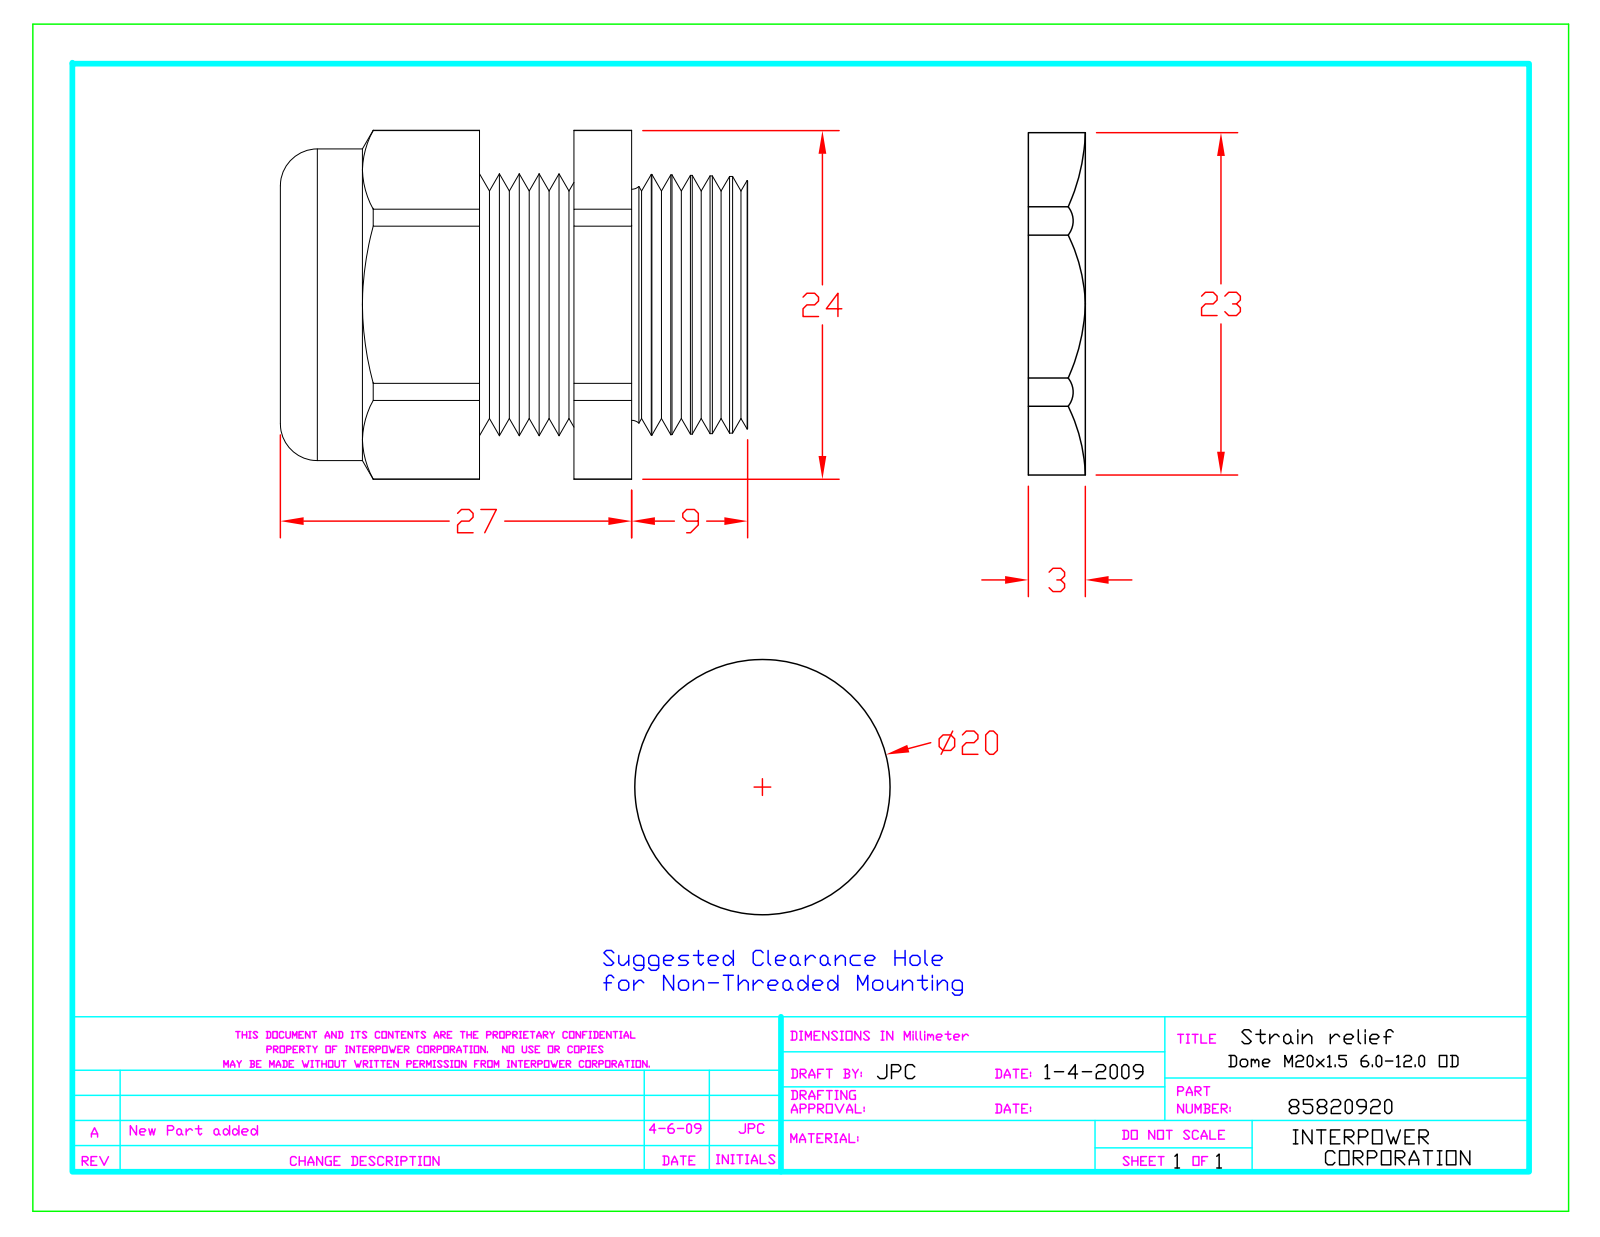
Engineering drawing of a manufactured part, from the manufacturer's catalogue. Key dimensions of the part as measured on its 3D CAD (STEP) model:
Part name (STEP PRODUCT): CD20MA
STEP written by: SolidWorks 2007 (CONFIG_CONTROL_DESIGN)
Units: inches
Bodies: 2 solids, 116 faces (20 planar, 24 cylindrical, 72 other)
Overall size (bounding box): 1.41 × 1.053 × 0.94
Volume: 0.514 in³ · Surface area: 10.49 in²
Round holes (diameter × count): ⌀0.51 ×1, ⌀0.671 ×1, ⌀0.79 ×1
Round bosses / shafts (diameter × count): ⌀0.94 ×1
Partial cylindrical surfaces — rounded edges, fillets, slot ends (radius × count): R0.526 ×1
Main face-to-face distances: 0.94, 0.354, 0.639, 0.285, 0.813, 0.459, 0.174, 1.163, 0.809, 0.524
